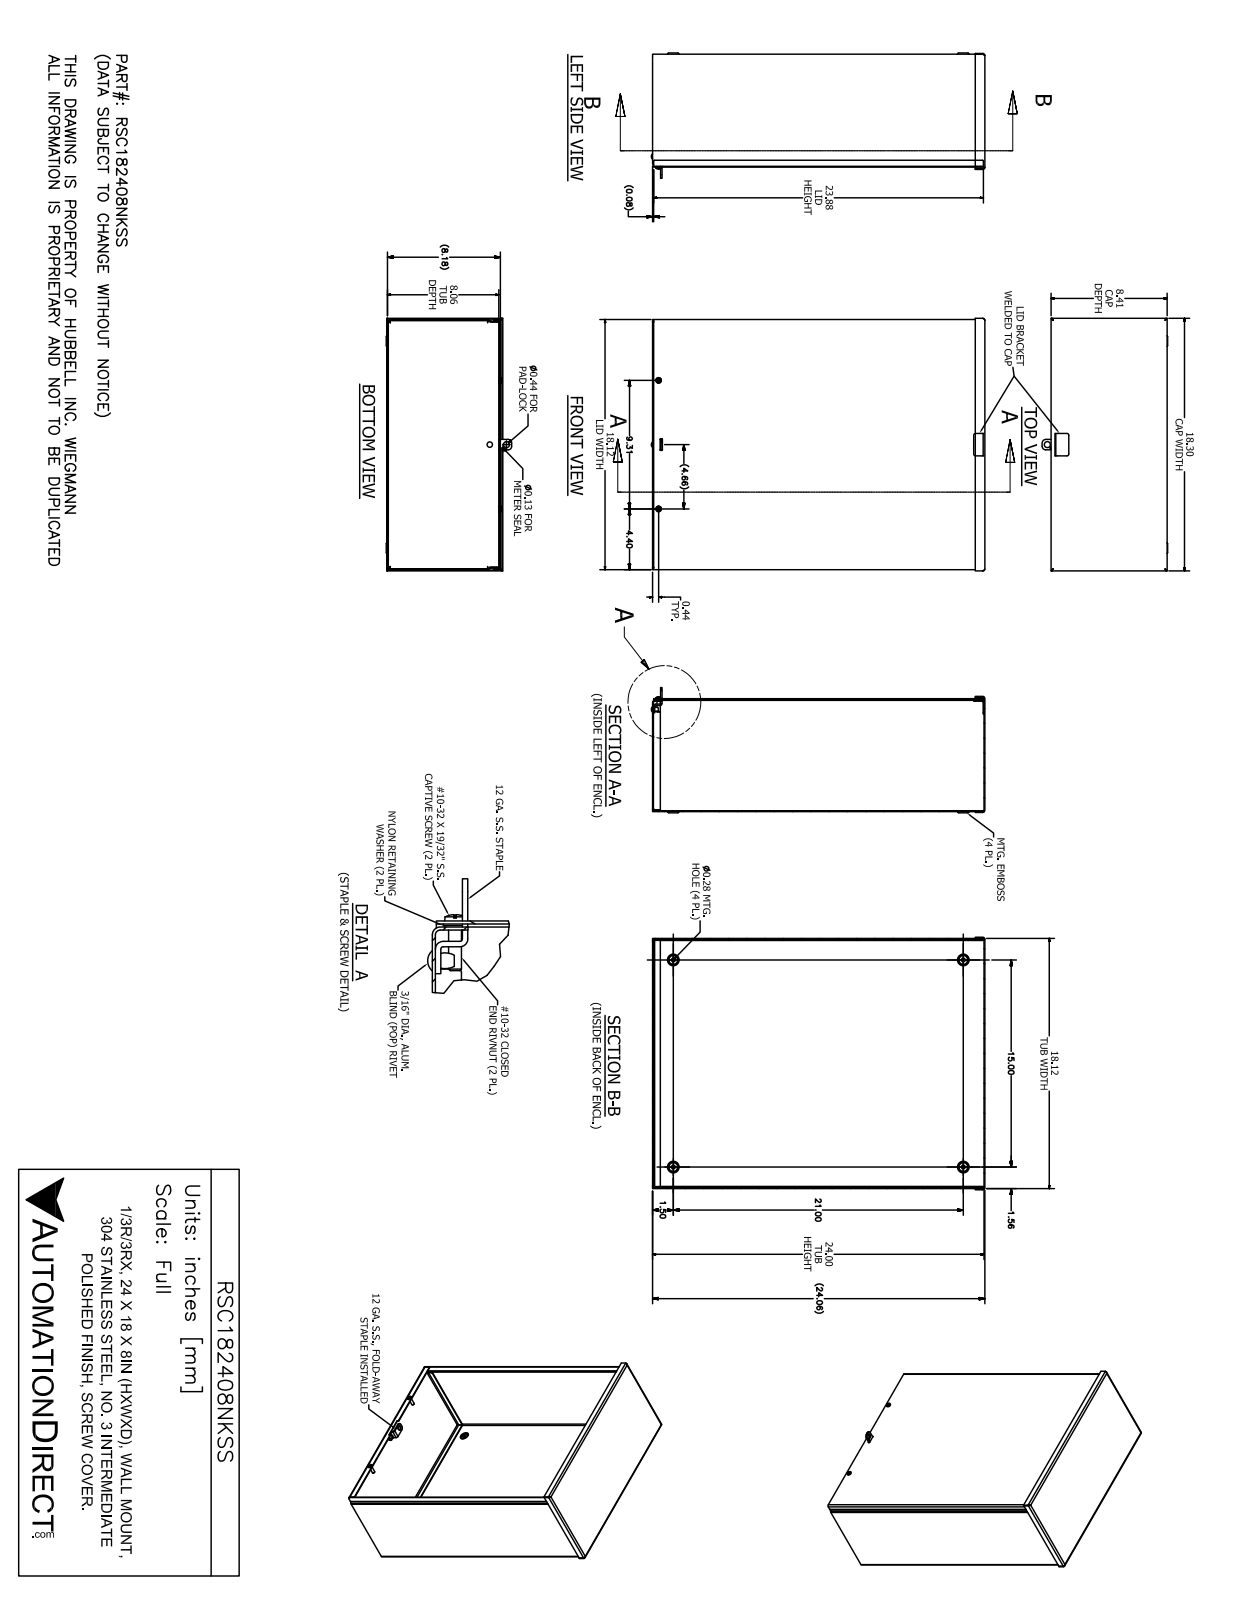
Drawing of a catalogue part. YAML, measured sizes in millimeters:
part_name: "RSC182408NKSS"
step_written_by: "SolidWorks 2017 (AUTOMOTIVE_DESIGN)"
units: millimeters
bodies: {solids: 13, faces: 383, planar: 199, cylindrical: 99, other: 85}
overall_size: [613.4, 464.8, 230.7]
volume: 1574000
surface_area: 2114000
round_holes:
  - {diameter: 6.4, count: 4}
  - {diameter: 7.1, count: 4}
  - {diameter: 4, count: 2}
  - {diameter: 5, count: 2}
  - {diameter: 6.5, count: 2}
  - {diameter: 7.1, count: 2}
  - {diameter: 3.2, count: 1}
  - {diameter: 5, count: 1}
  - {diameter: 5.1, count: 1}
  - {diameter: 11.1, count: 1}
round_bosses_or_shafts:
  - {diameter: 11.5, count: 2}
  - {diameter: 10.3, count: 2}
  - {diameter: 6.3, count: 2}
  - {diameter: 4.2, count: 2}
  - {diameter: 4.7, count: 1}
partial_cylinders:
  - {radius: 2.4, count: 17}
  - {radius: 3.9, count: 17}
  - {radius: 0.8, count: 6}
  - {radius: 3.2, count: 4}
  - {radius: 6.4, count: 4}
  - {radius: 1.2, count: 2}
  - {radius: 1.3, count: 2}
  - {radius: 1.6, count: 2}
face_to_face_distances: [1.5, 206.2, 207.7, 204.7, 458.7, 609.6, 460.2, 457.2, 611.1, 608.1]
hole_center_spacings: [77.1, 77.4, 236.6, 310, 310, 381, 533.4, 565]
